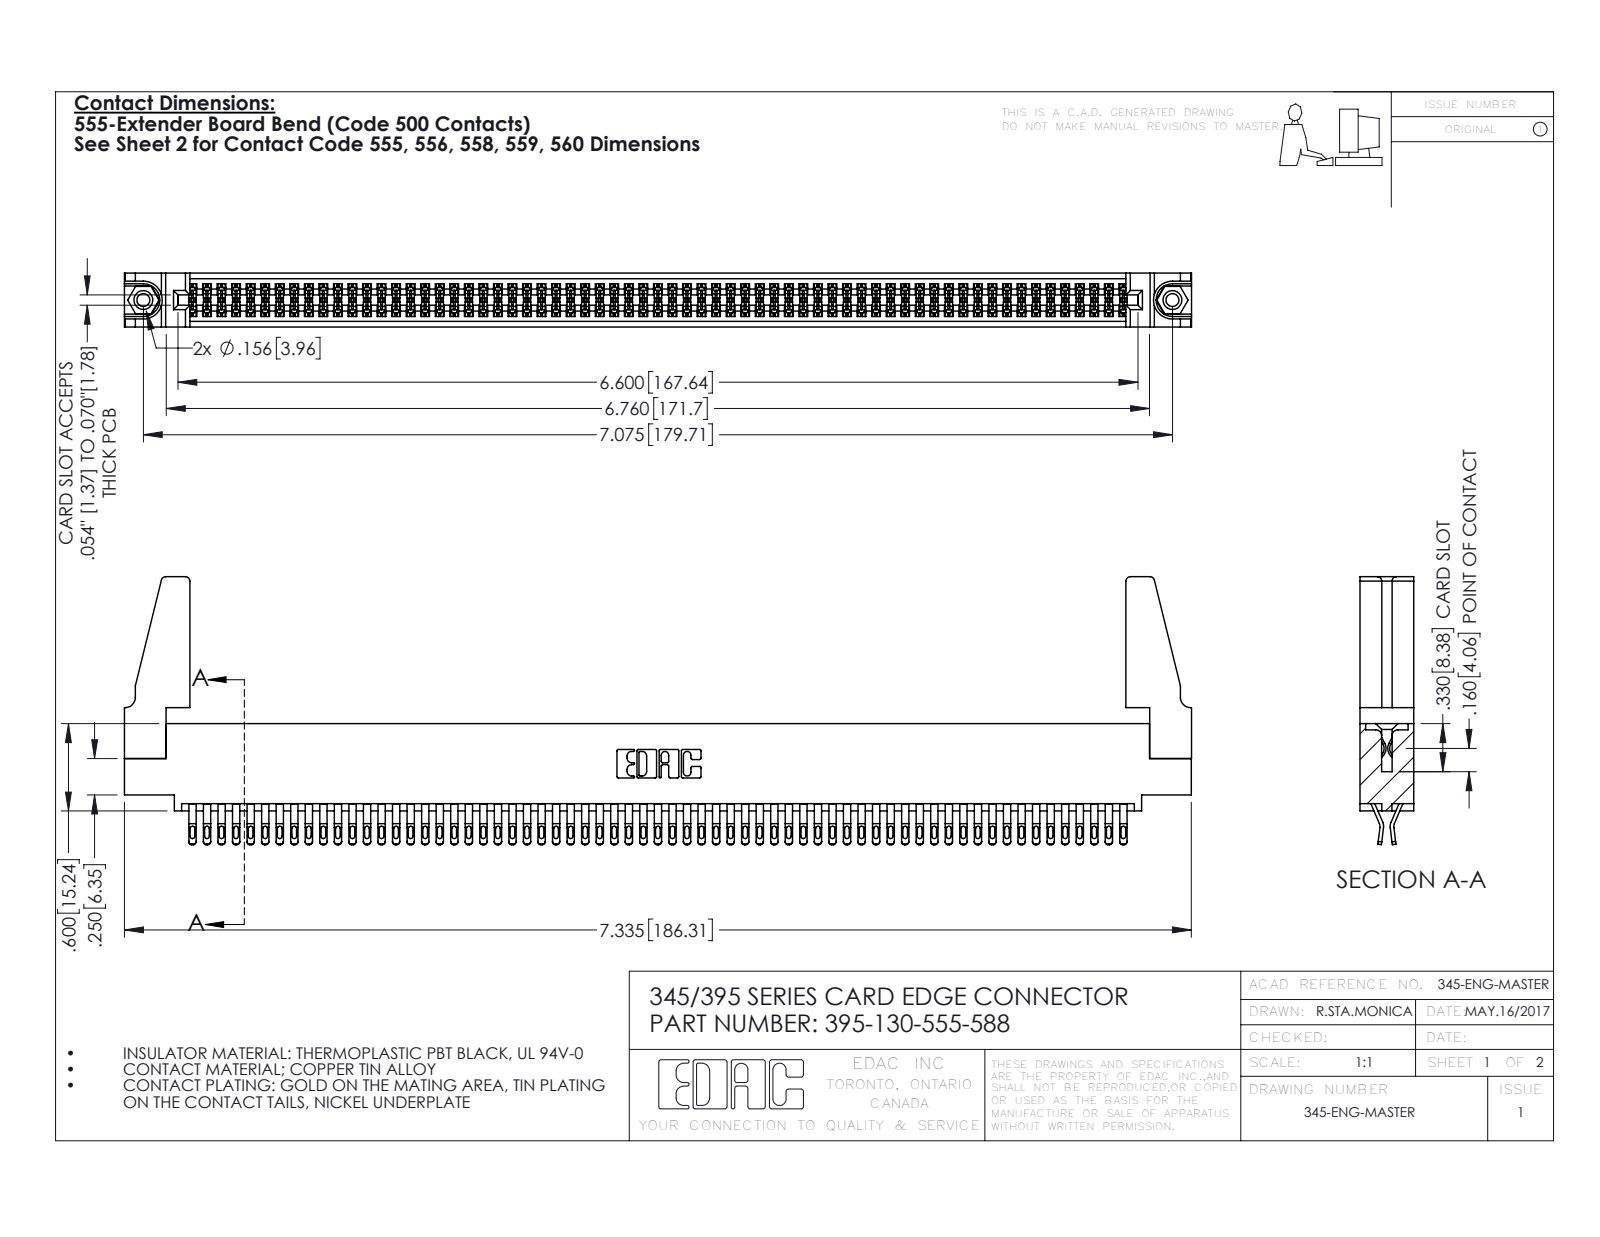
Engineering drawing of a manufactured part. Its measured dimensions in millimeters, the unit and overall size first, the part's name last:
Units: millimetres
Overall size (bounding box): 186.3 × 46.8 × 9.4
Round holes (diameter × count): ⌀2.3 ×2, ⌀3.2 ×2, ⌀4 ×2, ⌀1.6 ×1
Round bosses / shafts (diameter × count): ⌀3.9 ×2
Partial cylindrical surfaces — rounded edges, fillets, slot ends (radius × count): R0.4 ×325, R0.5 ×260, R0.2 ×195, R0.3 ×22, R0.8 ×8, R0.2 ×6, R0.8 ×6, R0.7 ×3
Main face-to-face distances: 1.8, 7.6, 9.4, 0.6, 5.1, 2.5, 6.9, 5.7, 4.4, 3.8
Hole centre spacings: 6.9, 173.7, 179.7
Volume: 21 880 mm³ · Surface area: 32 490 mm²
Bodies: 135 solids, 7534 faces (4186 planar, 3332 cylindrical, 16 other)
Part name (STEP PRODUCT): 345-220-078_345-220-088; 345-292-001_555 Tail; 345-250-001_345-250-001-102; 345 Part_0.110 Offset - 0.156 Dia-TH (+1 more)
STEP written by: SolidWorks 2016 (CONFIG_CONTROL_DESIGN)
